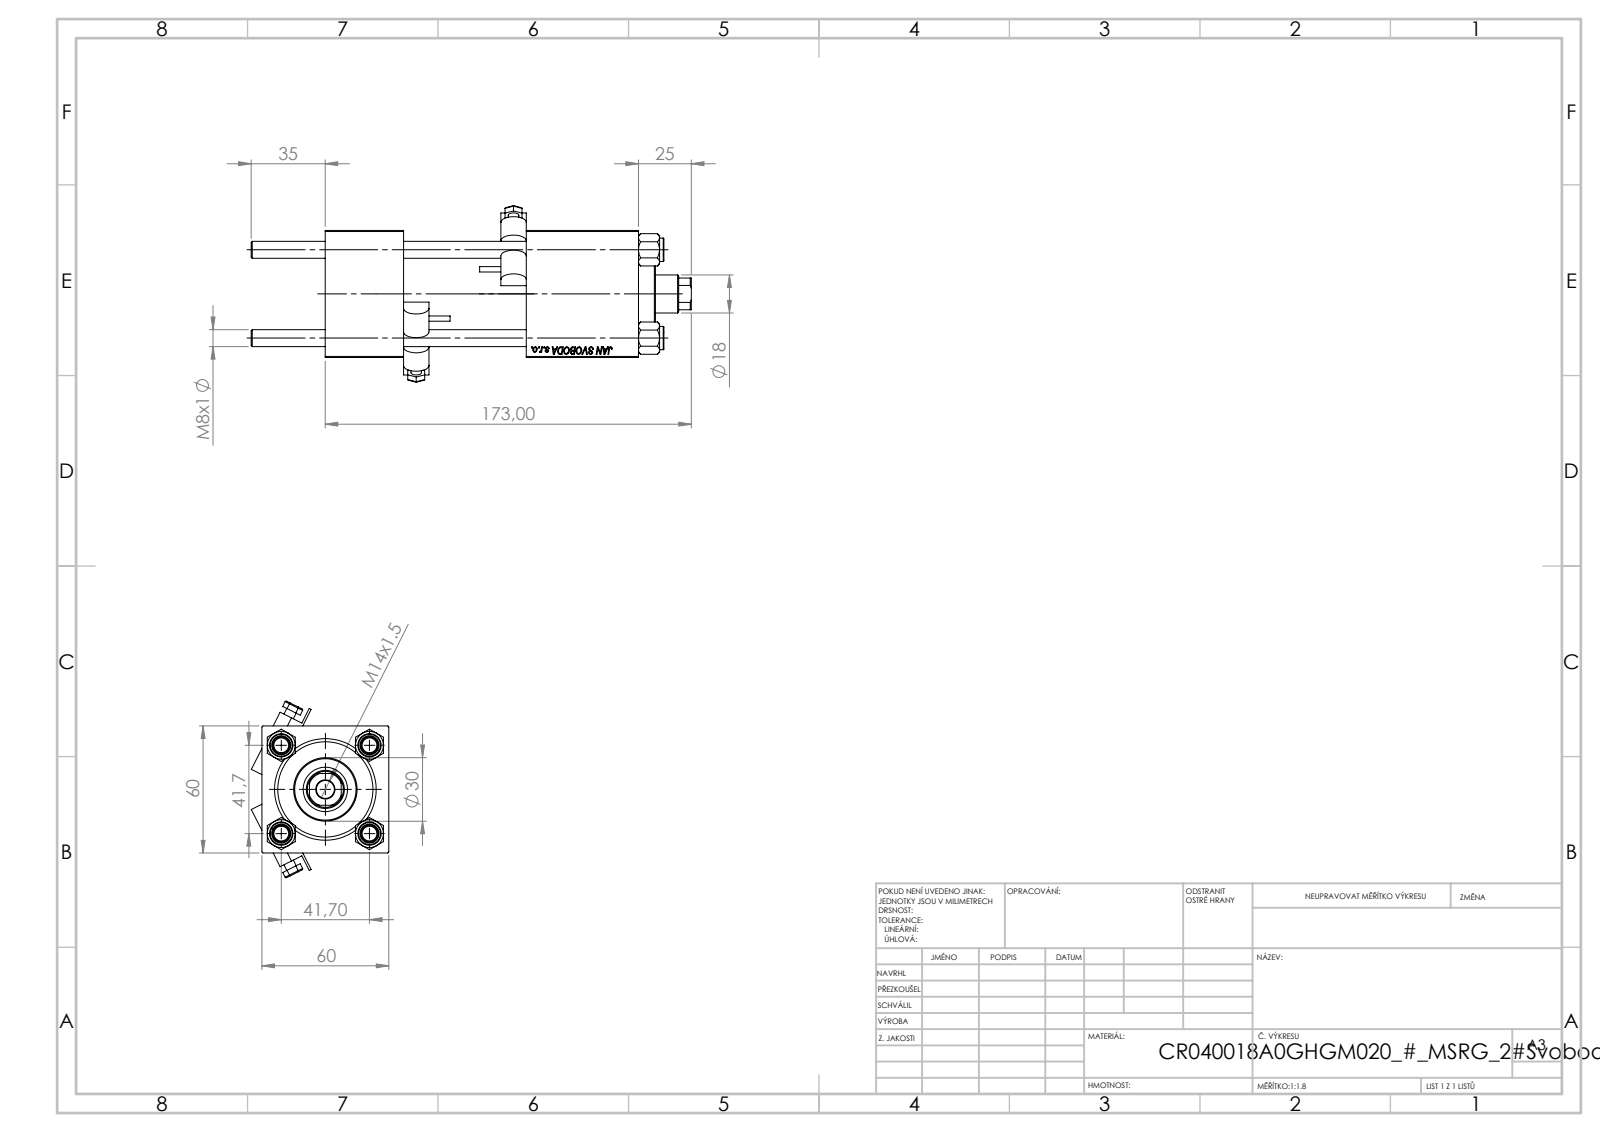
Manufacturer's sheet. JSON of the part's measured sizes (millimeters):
{"part_name": "V215CR_BODY_A; V215CR_VCP; MSRF_MSRG1; CR025_012_A_0_G_A_G_M_020_+#_##_TYCINKA (+2 more)", "step_written_by": "SolidWorks 2019 (CONFIG_CONTROL_DESIGN)", "units": "millimeters", "bodies": {"solids": 13, "faces": 1199, "planar": 557, "cylindrical": 106, "other": 536}, "overall_size": [208, 83.44, 64.97], "volume_mm3": 420973, "surface_area_mm2": 118299, "round_holes": [[8, 4], [7, 2], [16.66, 2], [24, 2], [8.5, 1], [18, 1], [21, 1], [31, 1], [40, 1], [45, 1]], "round_bosses_or_shafts": [[11, 4], [5, 2], [2.5, 2], [46, 1], [30, 1]], "partial_cylinders_radius": [[0.5, 12], [6, 4], [8.5, 1]], "face_to_face_distances": [60, 37, 111, 148, 58, 53, 95, 119.3, 82.3, 24.3], "hole_center_spacings": [29.49, 41.7, 58.97, 92.5]}
